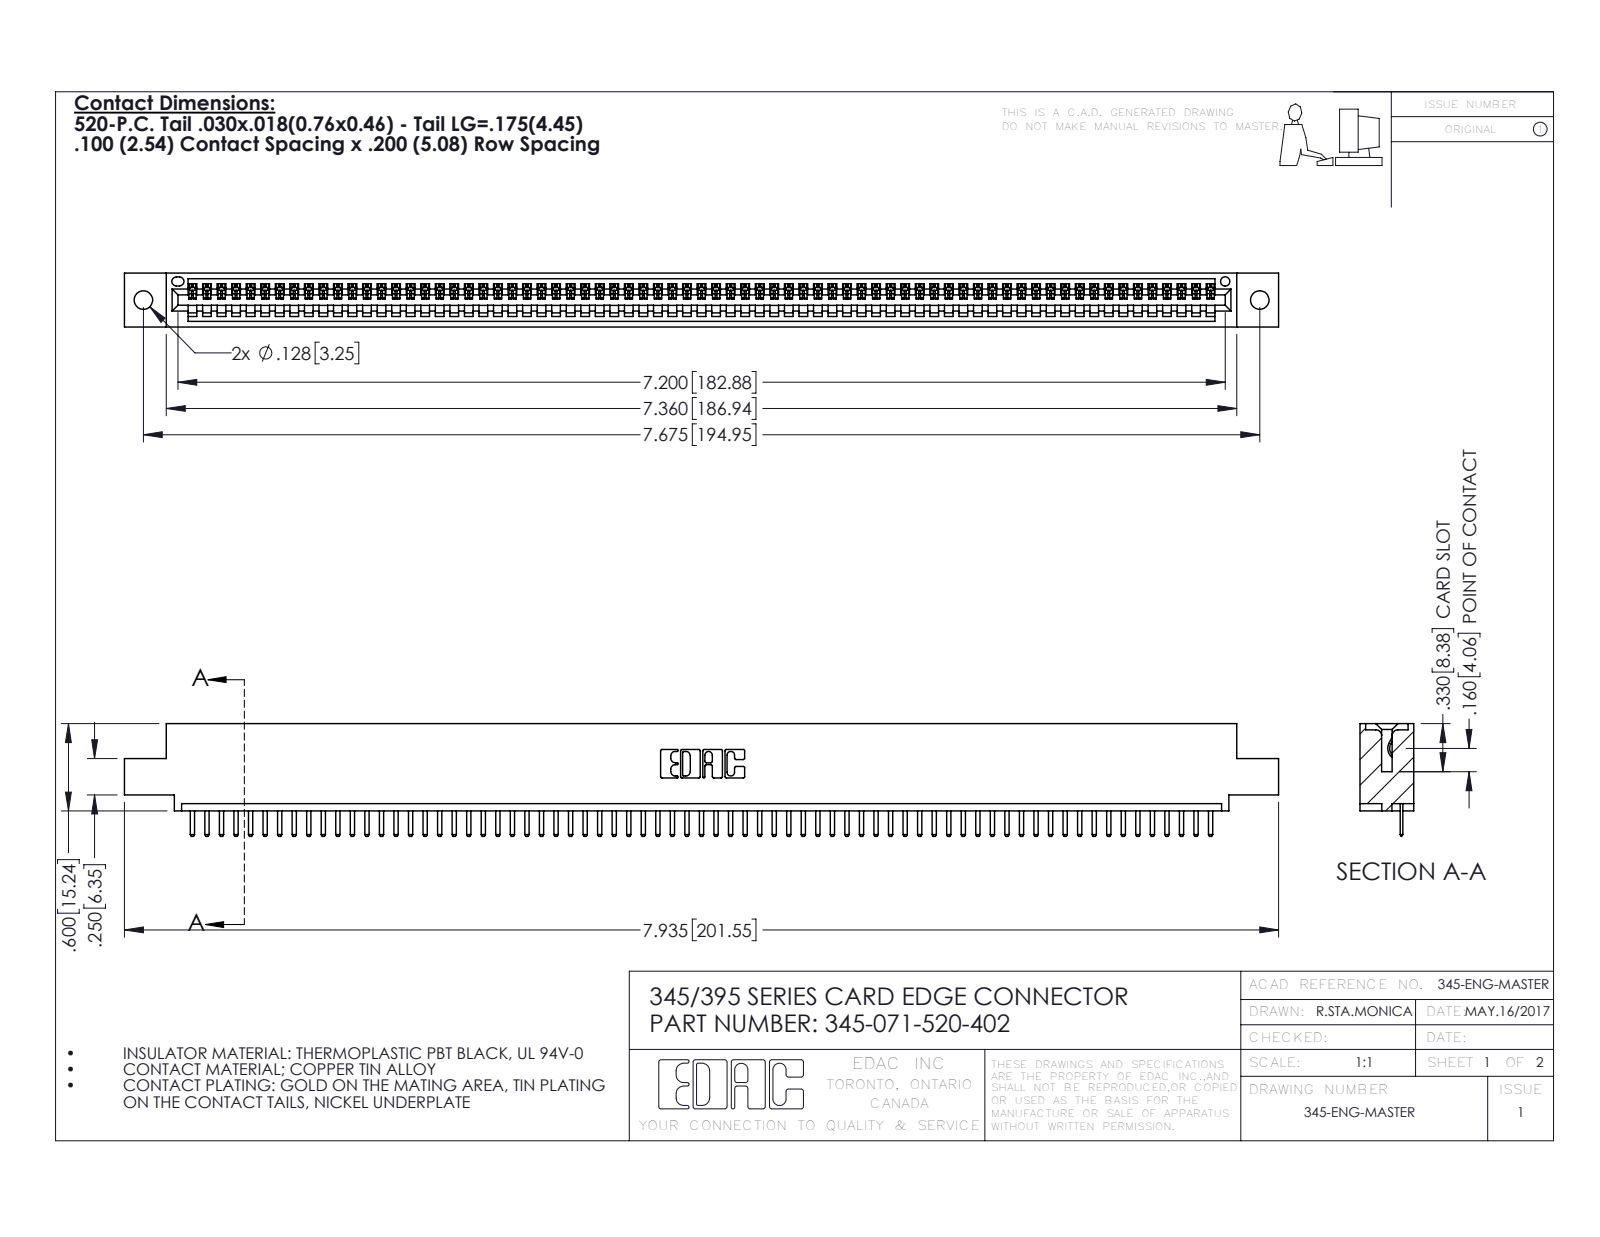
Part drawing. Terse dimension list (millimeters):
name: 345-071-520-402; 345-292-001_345-293-120; 345 Part_0.110 Offset - 0.128 Dia
written by: SolidWorks 2016 (CONFIG_CONTROL_DESIGN)
unit: mm
bodies: 72 solids, 4532 faces (3066 planar, 1466 cylindrical, 0 other)
size: 201.5 × 19.7 × 9.4
volume: 19 070 mm³; area: 24 880 mm²
holes: 2× ⌀3.3, 1× ⌀1.6
rounds: 144× R0.3, 142× R0.2, 22× R0.3, 6× R0.2, 6× R0.8, 3× R0.7, 2× R0.8, 2× R1
face distances: 1.8, 7.6, 9.4, 5.1, 2.5, 6.9, 0.6, 5.7, 1.8, 3.8
hole spacings: 6.9, 189, 194.9
